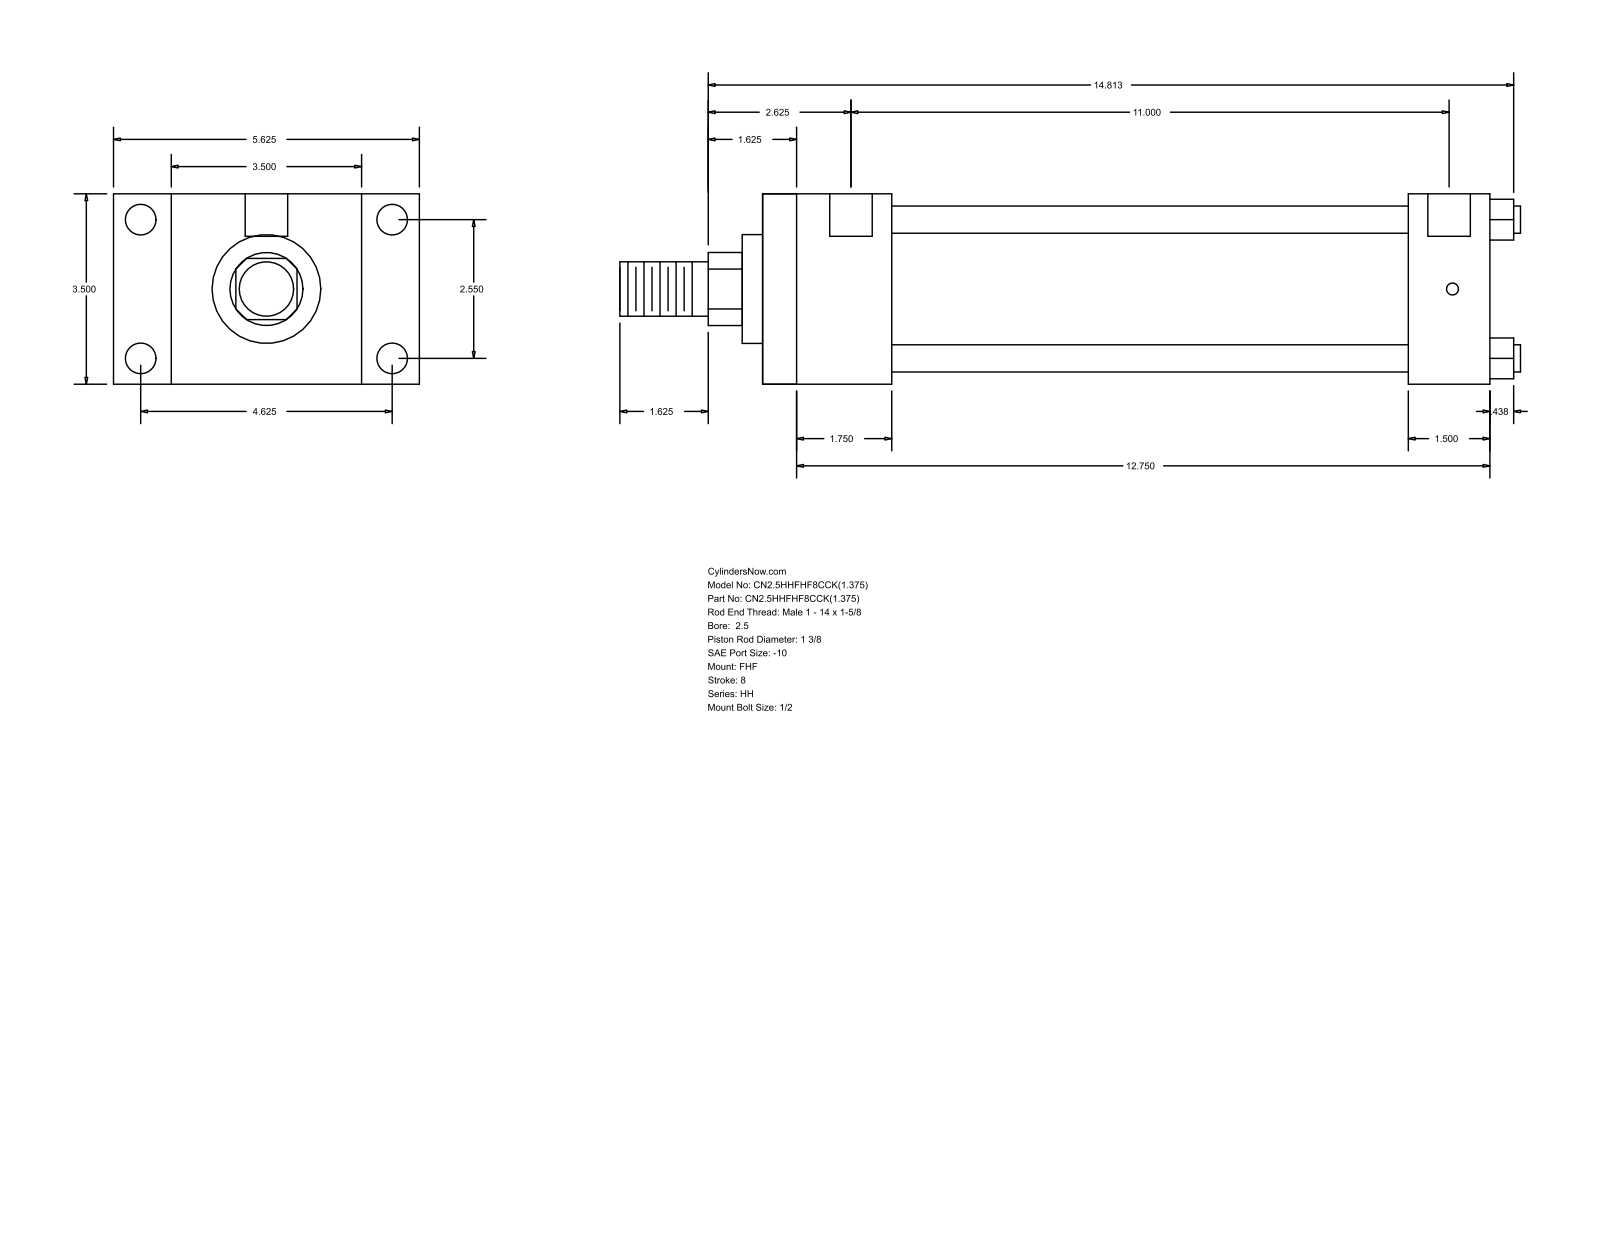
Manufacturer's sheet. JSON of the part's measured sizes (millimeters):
{"part_name": "HH_FHF__0250_1.375", "step_written_by": "GSSL Pune (CONFIG_CONTROL_DESIGN)", "units": "millimeters", "bodies": {"solids": 0, "faces": 88, "planar": 60, "cylindrical": 28, "other": 0}, "overall_size": [420.69, 142.88, 88.9], "round_holes": [[5.56, 4], [14.3, 4], [19.84, 2]], "round_bosses_or_shafts": [[12.7, 4], [73.03, 1], [50.8, 1], [34.92, 1], [25.4, 1]], "partial_cylinders_radius": [[17.06, 1]], "face_to_face_distances": [88.9, 60.32, 26.99, 115.89, 339.72, 279.4, 142.88, 301.62, 241.3, 38.1], "hole_center_spacings": [64.76, 117.48, 134.15, 282.57, 1.58, 1.59, 279.4, 280.98]}
